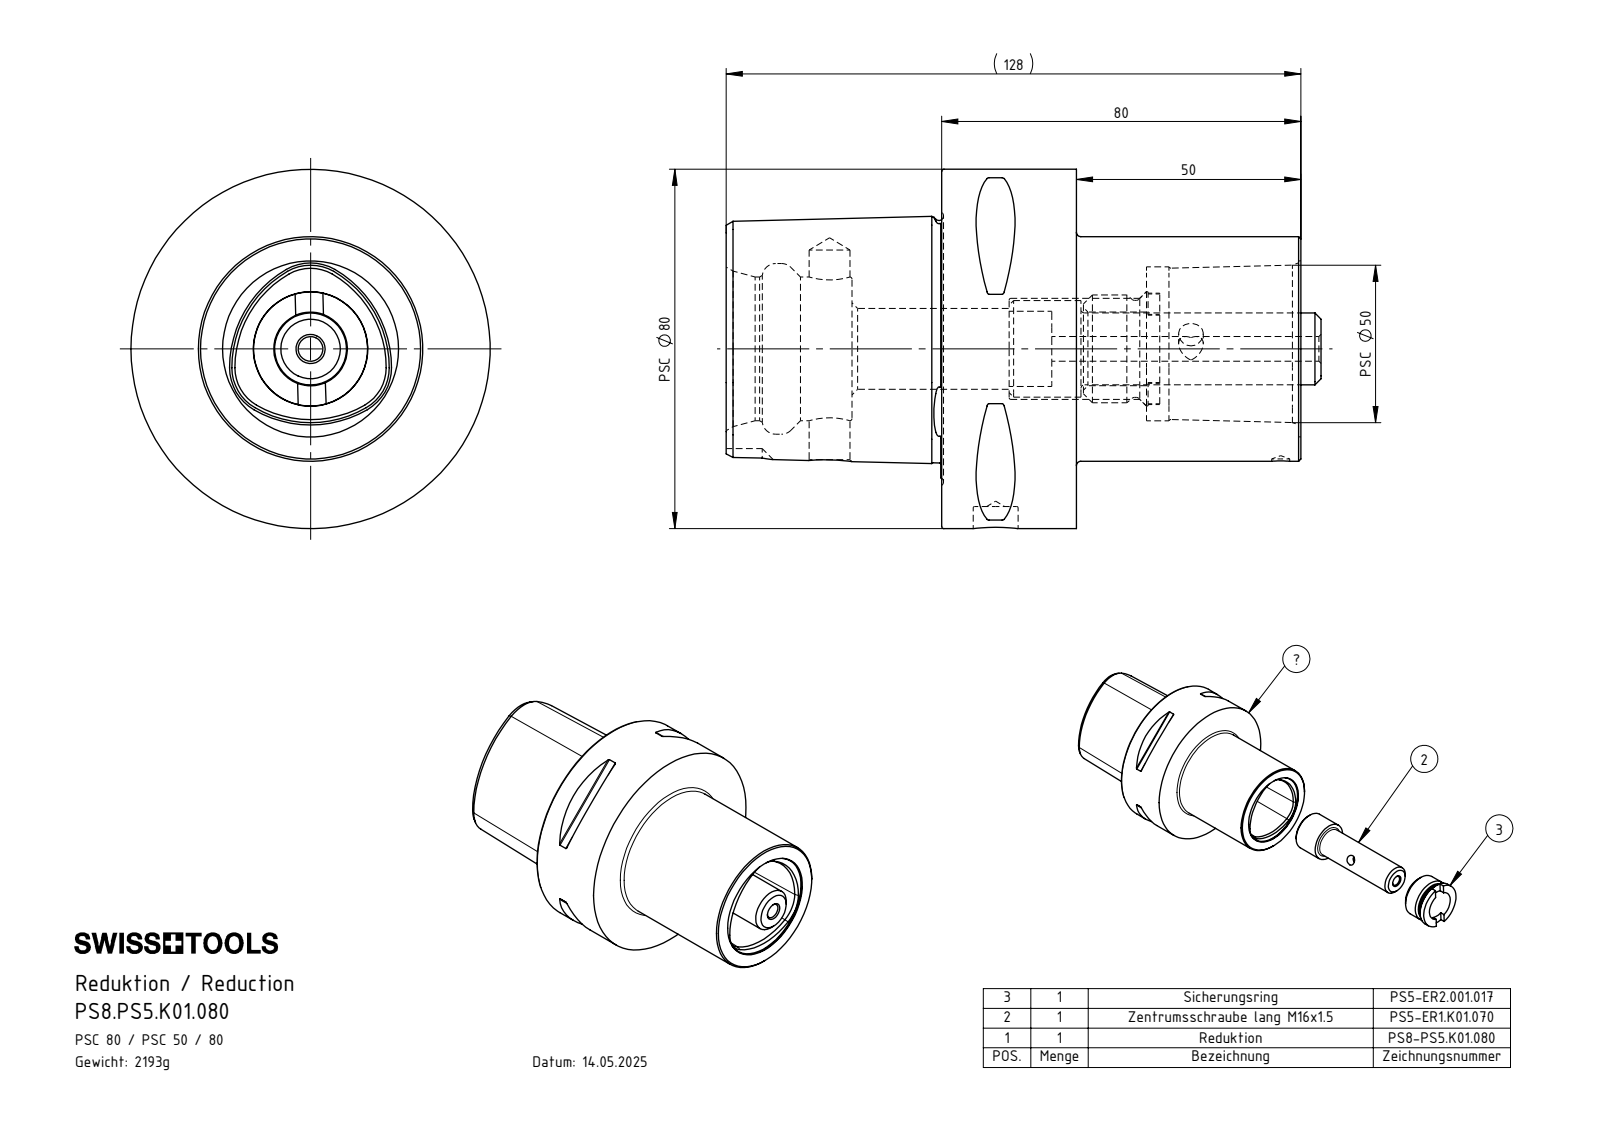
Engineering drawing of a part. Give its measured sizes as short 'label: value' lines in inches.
name: PS5-ER1.K01.070_A_PreviewCfg; PS8-PS5.K01.080_A; PS5-ER2.001.017_A; PS8.PS5.K01.080
written by: SolidWorks 2022 (AUTOMOTIVE_DESIGN)
unit: in
bodies: 3 solids, 244 faces (36 planar, 71 cylindrical, 137 other)
size: 5.217 × 3.15 × 3.15
volume: 18.35 in³; area: 80.87 in²
holes: 2× ⌀0.217, 1× ⌀0.157, 1× ⌀0.358, 1× ⌀0.394, 1× ⌀0.646, 1× ⌀0.709, 1× ⌀0.886, 1× ⌀1.26, 1× ⌀1.496, 1× ⌀1.543
bosses: 1× ⌀3.15, 1× ⌀1.969, 1× ⌀1, 1× ⌀0.945, 1× ⌀0.85, 1× ⌀0.846, 1× ⌀0.63
rounds: 8× R0.02, 7× R0.236, 6× R0.091, 3× R0.39, 3× R0.96
face distances: 1.89, 5.039, 3.15, 1.281, 1.102, 0.787, 3.937, 3.685, 2.583, 1.795
hole spacings: 1.457, 2.5, 3.957
